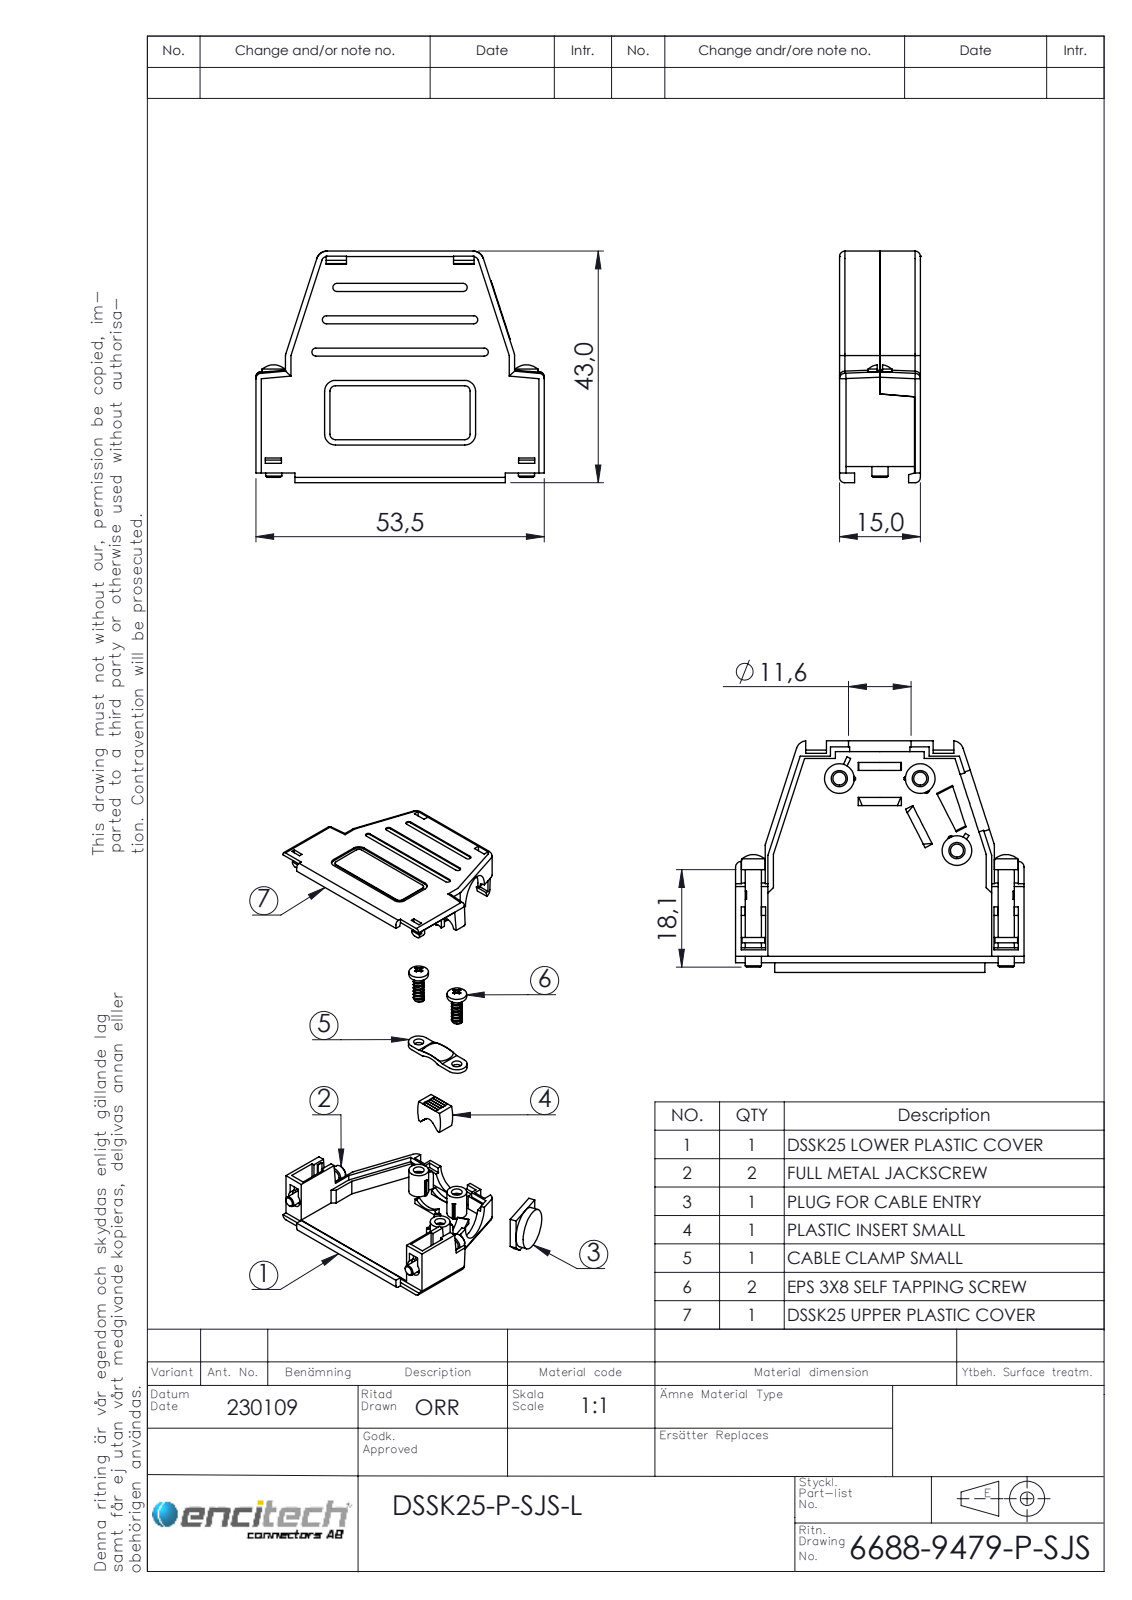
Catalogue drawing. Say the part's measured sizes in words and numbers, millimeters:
The part is named "6688-9479-P-SJS; 6855-0109-01; 6822-0128-01; 6826-0133-01 (+4 more)". Its 3-D file was written by "SolidWorks 2021 (AUTOMOTIVE_DESIGN)". It is 11 solids with 781 faces: 511 planar, 209 cylindrical and 61 other. Overall it measures 53.5 by 43 by 15 millimeters. Its volume is 10 437 cubic millimeters and its surface area 15 110 square millimeters. Round holes: 3 of diameter 2.4, 3 of diameter 3, 2 of diameter 2.8, 2 of diameter 11.6, 1 of diameter 3.5, 1 of diameter 9.4. Round bosses or shafts: 3 of diameter 5.5, 2 of diameter 5.45, 2 of diameter 4.4, 2 of diameter 4.2, 2 of diameter 3, 2 of diameter 2.46, 1 of diameter 11.4. Partial cylindrical surfaces (rounded edges, fillets, slot ends): 40 of radius 1, 14 of radius 2, 6 of radius 0.75, 5 of radius 5.8, 4 of radius 0.1, 4 of radius 0.25, 4 of radius 0.5, 2 of radius 1.2. The main face-to-face distances are 1.7, 13.3, 11.6, 15, 1.5, 14.8, 13.1, 2, 1.1, 5.8. The hole center spacings are 7.57, 15, 18.92, 25.58.
